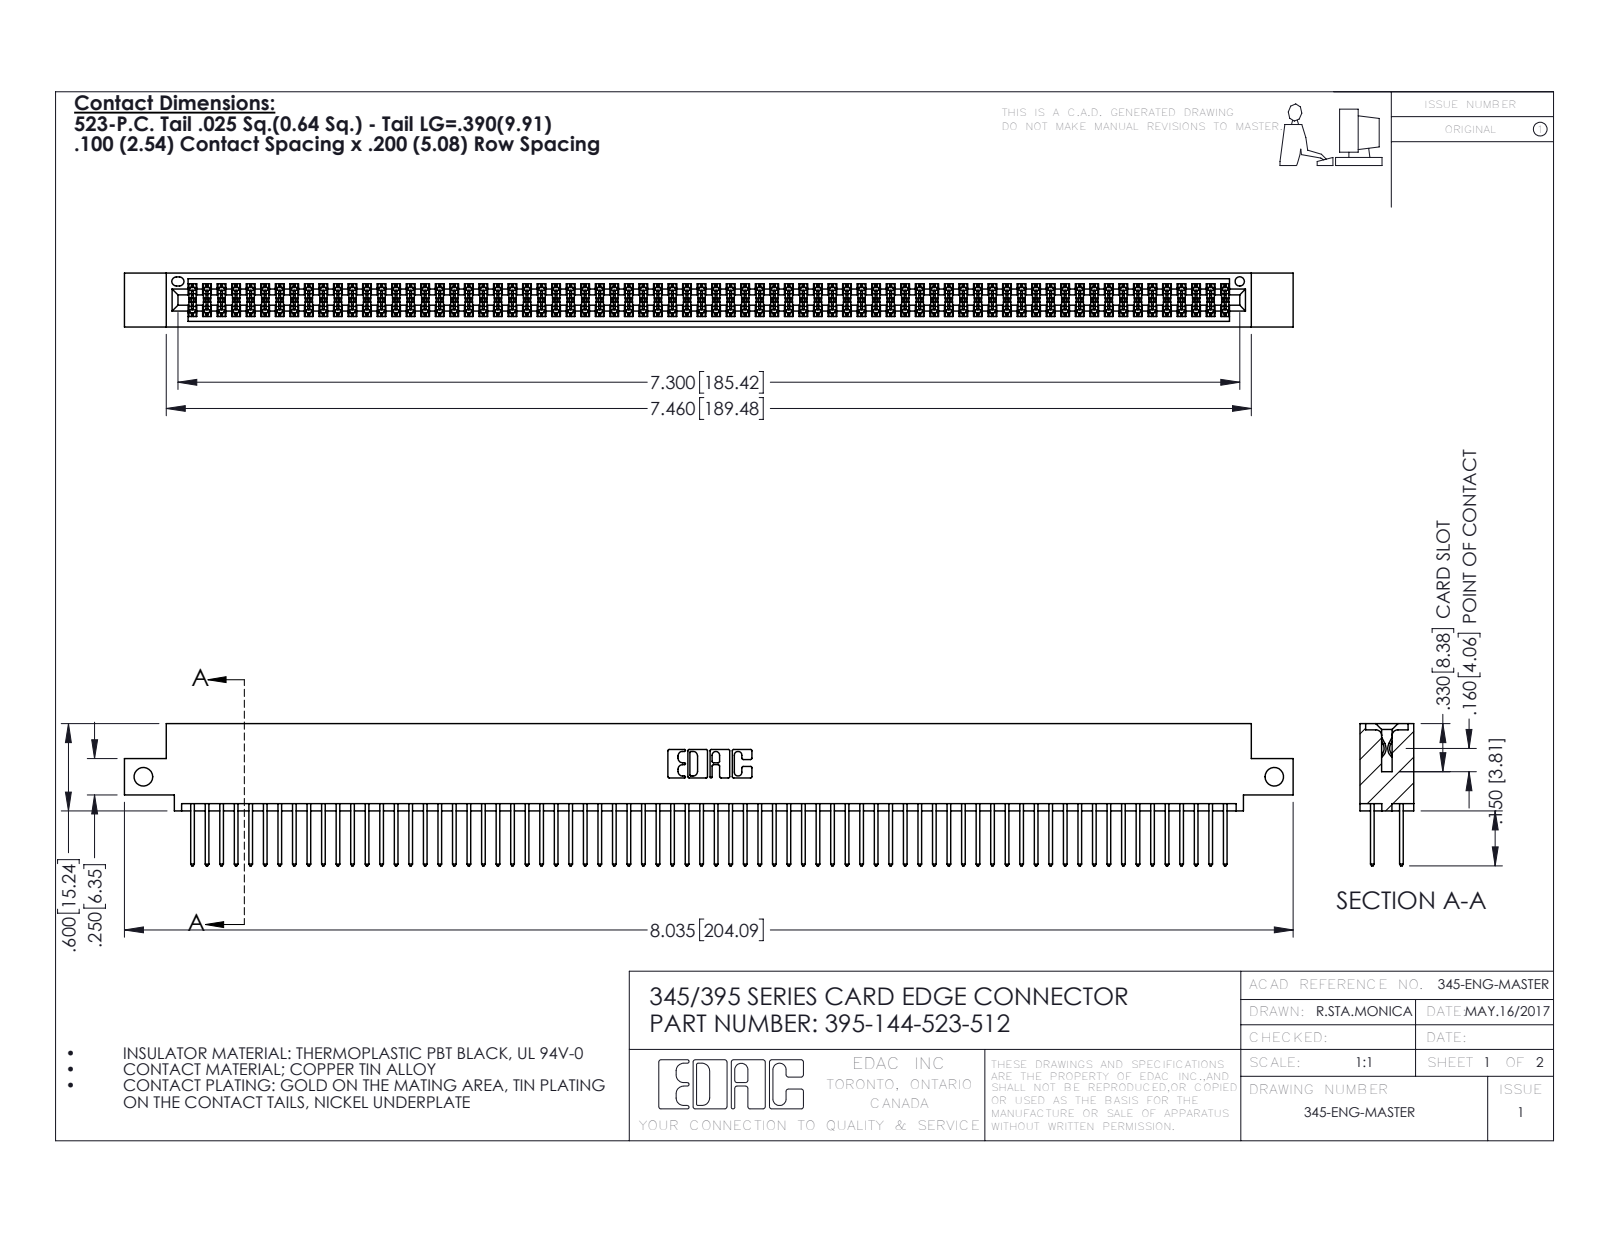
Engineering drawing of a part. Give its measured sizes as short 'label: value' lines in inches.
name: 345-292-001_345-293-123; 345 Part_0.110 Offset - Side Mount; 395-144-523-512
written by: SolidWorks 2016 (CONFIG_CONTROL_DESIGN)
unit: in
bodies: 145 solids, 7330 faces (4836 planar, 2494 cylindrical, 0 other)
size: 8.035 × 0.977 × 0.37
volume: 1.235 in³; area: 49.26 in²
holes: 2× ⌀0.128, 1× ⌀0.064
rounds: 216× R0.006, 144× R0.01, 22× R0.01, 6× R0.007, 6× R0.031, 3× R0.026, 2× R0.014, 2× R0.019
face distances: 0.072, 0.298, 0.2, 0.098, 0.272, 0.025, 0.37, 0.225, 0.175, 0.149
hole spacings: 7.775
